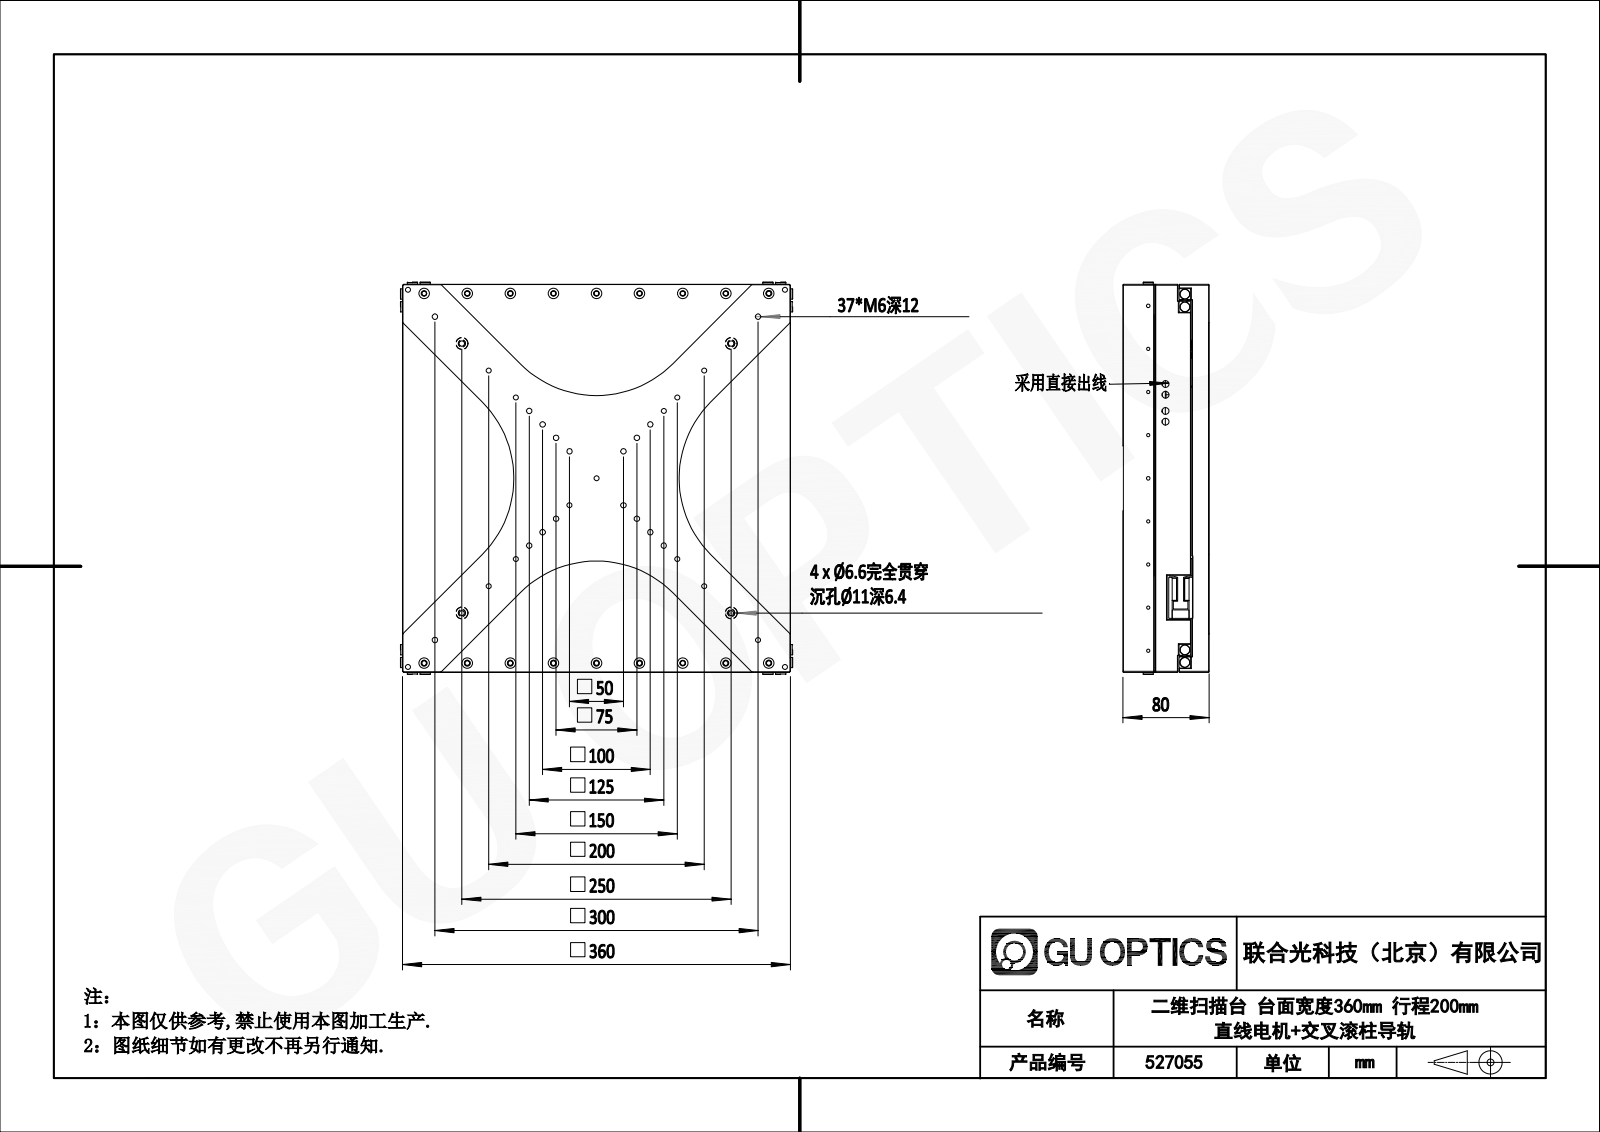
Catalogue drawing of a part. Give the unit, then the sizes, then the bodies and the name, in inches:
Units: inches
Overall size (bounding box): 14.331 × 14.331 × 3.15
Round holes (diameter × count): ⌀0.374 ×8, ⌀0.256 ×4
Round bosses / shafts (diameter × count): ⌀0.197 ×37, ⌀0.394 ×36, ⌀0.13 ×18, ⌀0.217 ×12, ⌀0.315 ×6, ⌀0.26 ×4, ⌀0.114 ×4
Partial cylindrical surfaces — rounded edges, fillets, slot ends (radius × count): R0.008 ×14, R0.512 ×8, R3.937 ×4, R5.906 ×4
Main face-to-face distances: 0.039, 1.378, 2.52, 0.02, 0.433, 0.866, 1.339, 2.48, 0.472, 0.906
Hole centre spacings: 0.465, 12.992, 0.394, 0.984, 12.528, 13.457, 0.591, 1.378
Bodies: 0 solids, 712 faces (475 planar, 193 cylindrical, 44 other)
Part name (STEP PRODUCT): 527055
STEP written by: SolidWorks 2020 (CONFIG_CONTROL_DESIGN)
